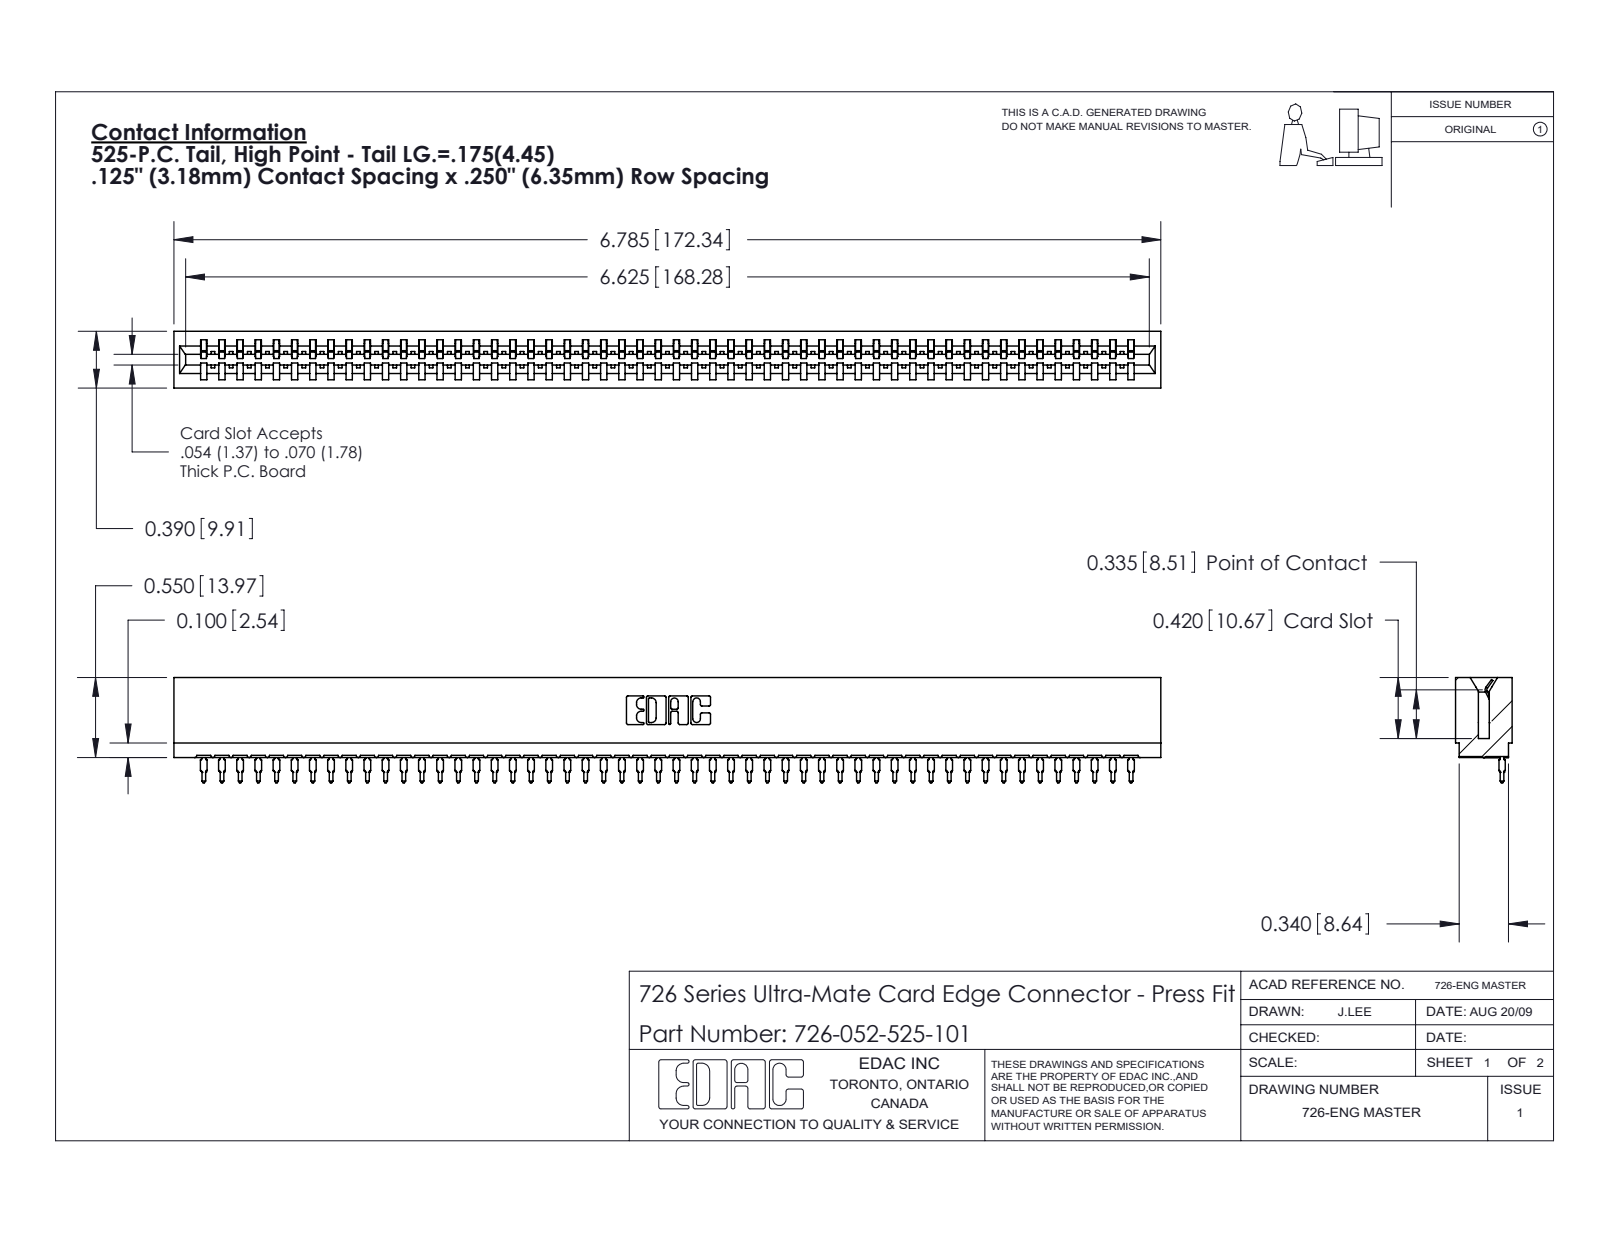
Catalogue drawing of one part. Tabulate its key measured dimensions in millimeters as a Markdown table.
| quantity | value |
| --- | --- |
| part name | 726 Part_.515 Slot Depth - 01; 746-292-001_525; 726-052-525-101 |
| STEP written by | SolidWorks 2020 (CONFIG_CONTROL_DESIGN) |
| units | millimeters |
| bodies | 53 solids, 5713 faces (3331 planar, 1030 cylindrical, 1352 other) |
| overall size | 172.3 × 18.4 × 9.9 |
| volume | 15 300 mm³ |
| surface area | 23 200 mm² |
| partial cylindrical surfaces (radius × count) | 0.5 × 104, 0.4 × 53, 0.3 × 22, 0.2 × 6, 0.8 × 6, 0.1 × 4, 0.3 × 4, 0.7 × 3 |
| main face-to-face distances | 1.4, 8.5, 9.9, 0.6, 7.8, 6.4, 7, 9.3, 0.8, 4.4 |
